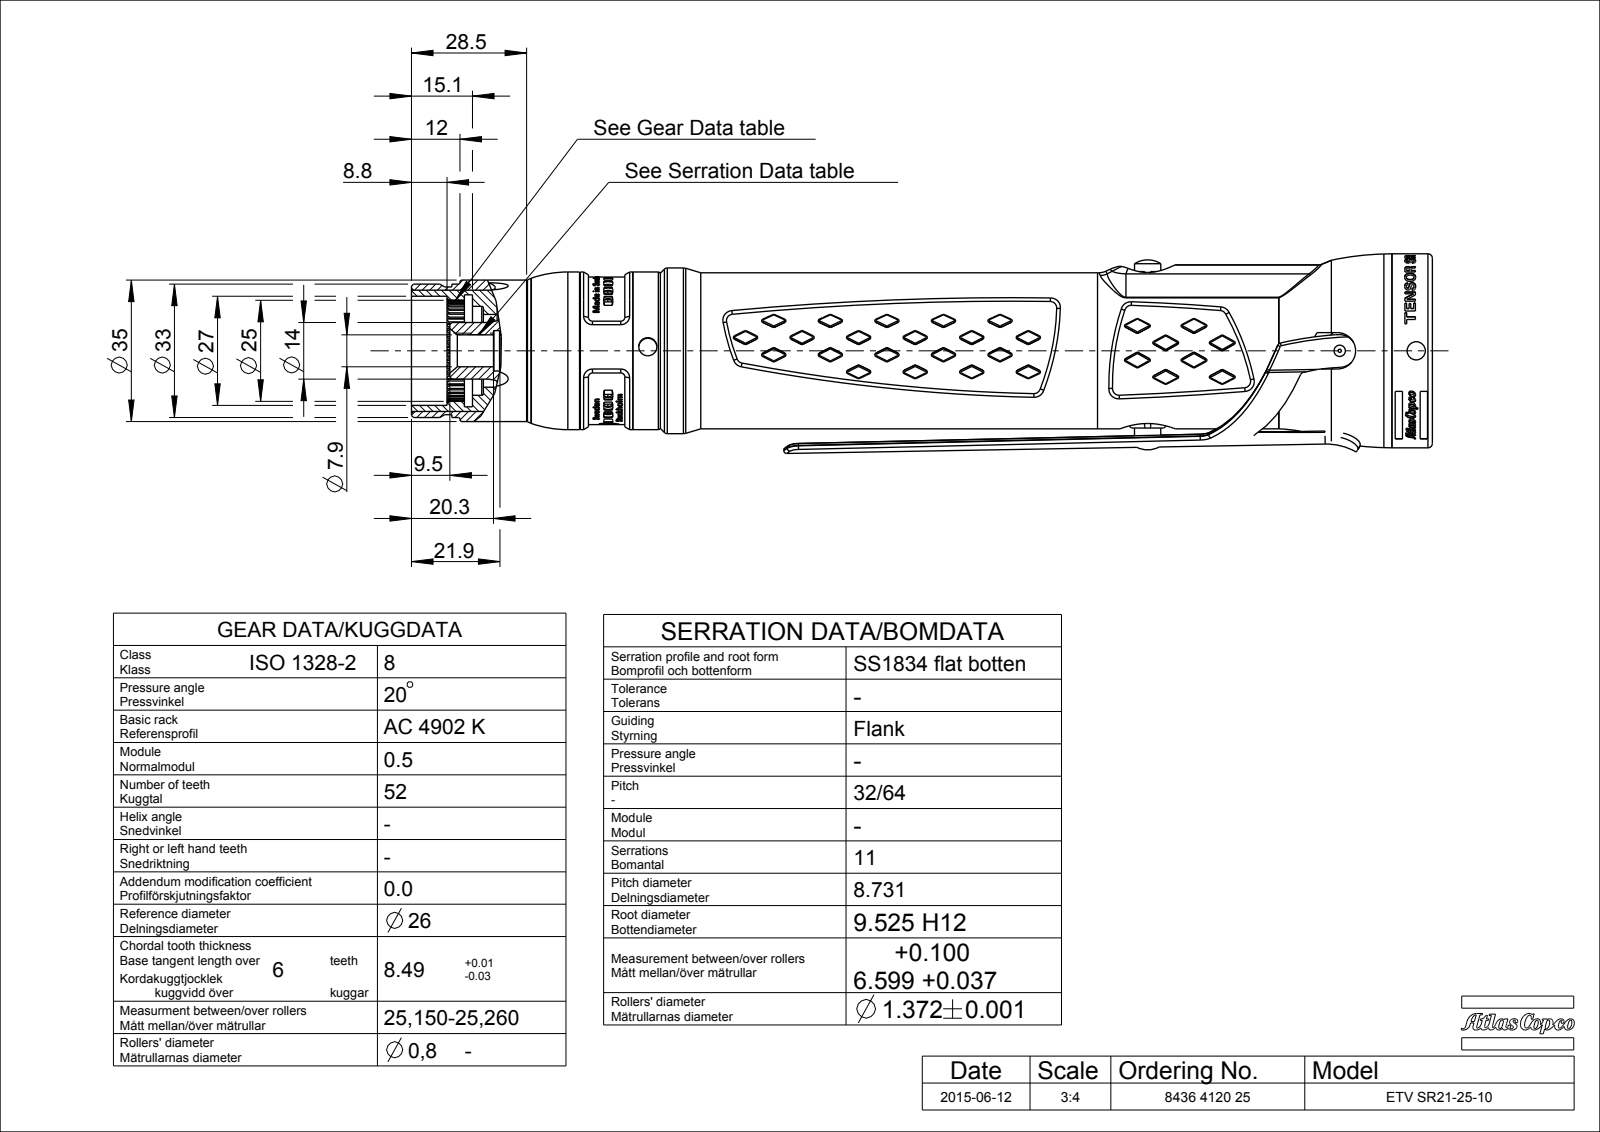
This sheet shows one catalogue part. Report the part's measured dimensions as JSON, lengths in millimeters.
{"part_name": "4220410004; 4220011402; 4220405381_ASM; 4220406381_ASM (+8 more)", "step_written_by": "PRO/ENGINEER BY PARAMETRIC TECHNOLOGY CORPORATION, 2011410 (CONFIG_CONTROL_DESIGN)", "units": "millimeters", "bodies": {"solids": 60, "faces": 4824, "planar": 1605, "cylindrical": 975, "other": 2244}, "overall_size": [311.57, 54.8, 48], "volume_mm3": 114140, "surface_area_mm2": 136786, "round_holes": [[3.27, 12], [2.64, 11], [3.6, 11], [3.2, 9], [1, 8], [4.5, 8], [2.6, 4], [2.8, 4], [1.5, 3], [2.5, 2], [3, 2], [6.5, 2]], "round_bosses_or_shafts": [[2.54, 4], [1.9, 4], [4.6, 3], [4, 3], [3.05, 3], [2.55, 3], [2.3, 3], [2.2, 3]], "partial_cylinders_radius": [[0.5, 88], [0.4, 32], [1, 20], [0.2, 8], [0.45, 8], [0.75, 8], [2, 7], [3, 4]], "face_to_face_distances": [2.5, 1.2, 21, 0.5, 57.3, 189, 168, 1.5, 23.07, 186.5], "hole_center_spacings": [1.5, 2.6, 4.48, 9.75, 13.79, 15, 21.21, 3]}
